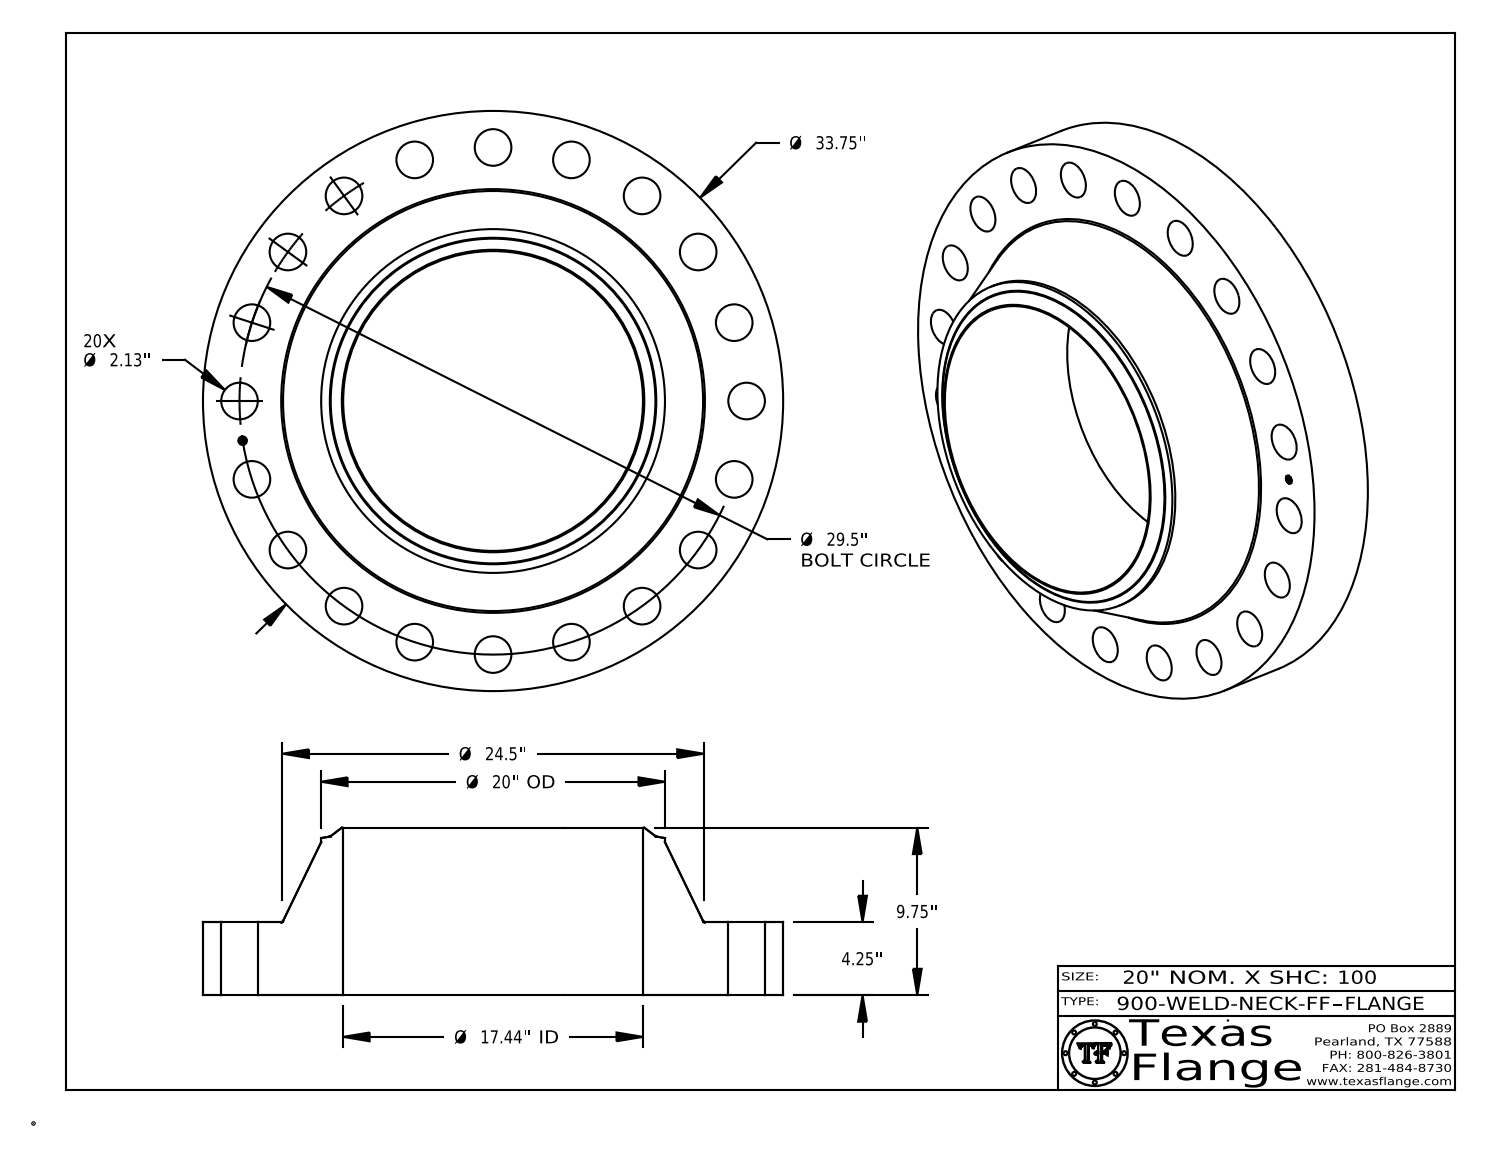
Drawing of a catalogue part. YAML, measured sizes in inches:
part_name: "900-WELD-NECK-FF"
step_written_by: "CATIA V5 STEP AP214 (AUTOMOTIVE_DESIGN)"
units: inches
bodies: {solids: 1, faces: 444, planar: 368, cylindrical: 66, other: 10}
overall_size: [33.75, 33.75, 9.75]
volume: 3224
surface_area: 2951
round_holes:
  - {diameter: 2.13, count: 20}
  - {diameter: 0.495, count: 1}
  - {diameter: 17.438, count: 1}
round_bosses_or_shafts:
  - {diameter: 0.03, count: 8}
  - {diameter: 33.75, count: 1}
  - {diameter: 20, count: 1}
  - {diameter: 0.39, count: 1}
face_to_face_distances: [4.25, 9.75, 5.5, 4.235, 0.015, 5.515, 0.148, 0.145, 0.027, 0.096]
hole_center_spacings: [14.75, 29.137, 4.615, 17.34, 20.859, 23.866, 26.285, 9.116]
